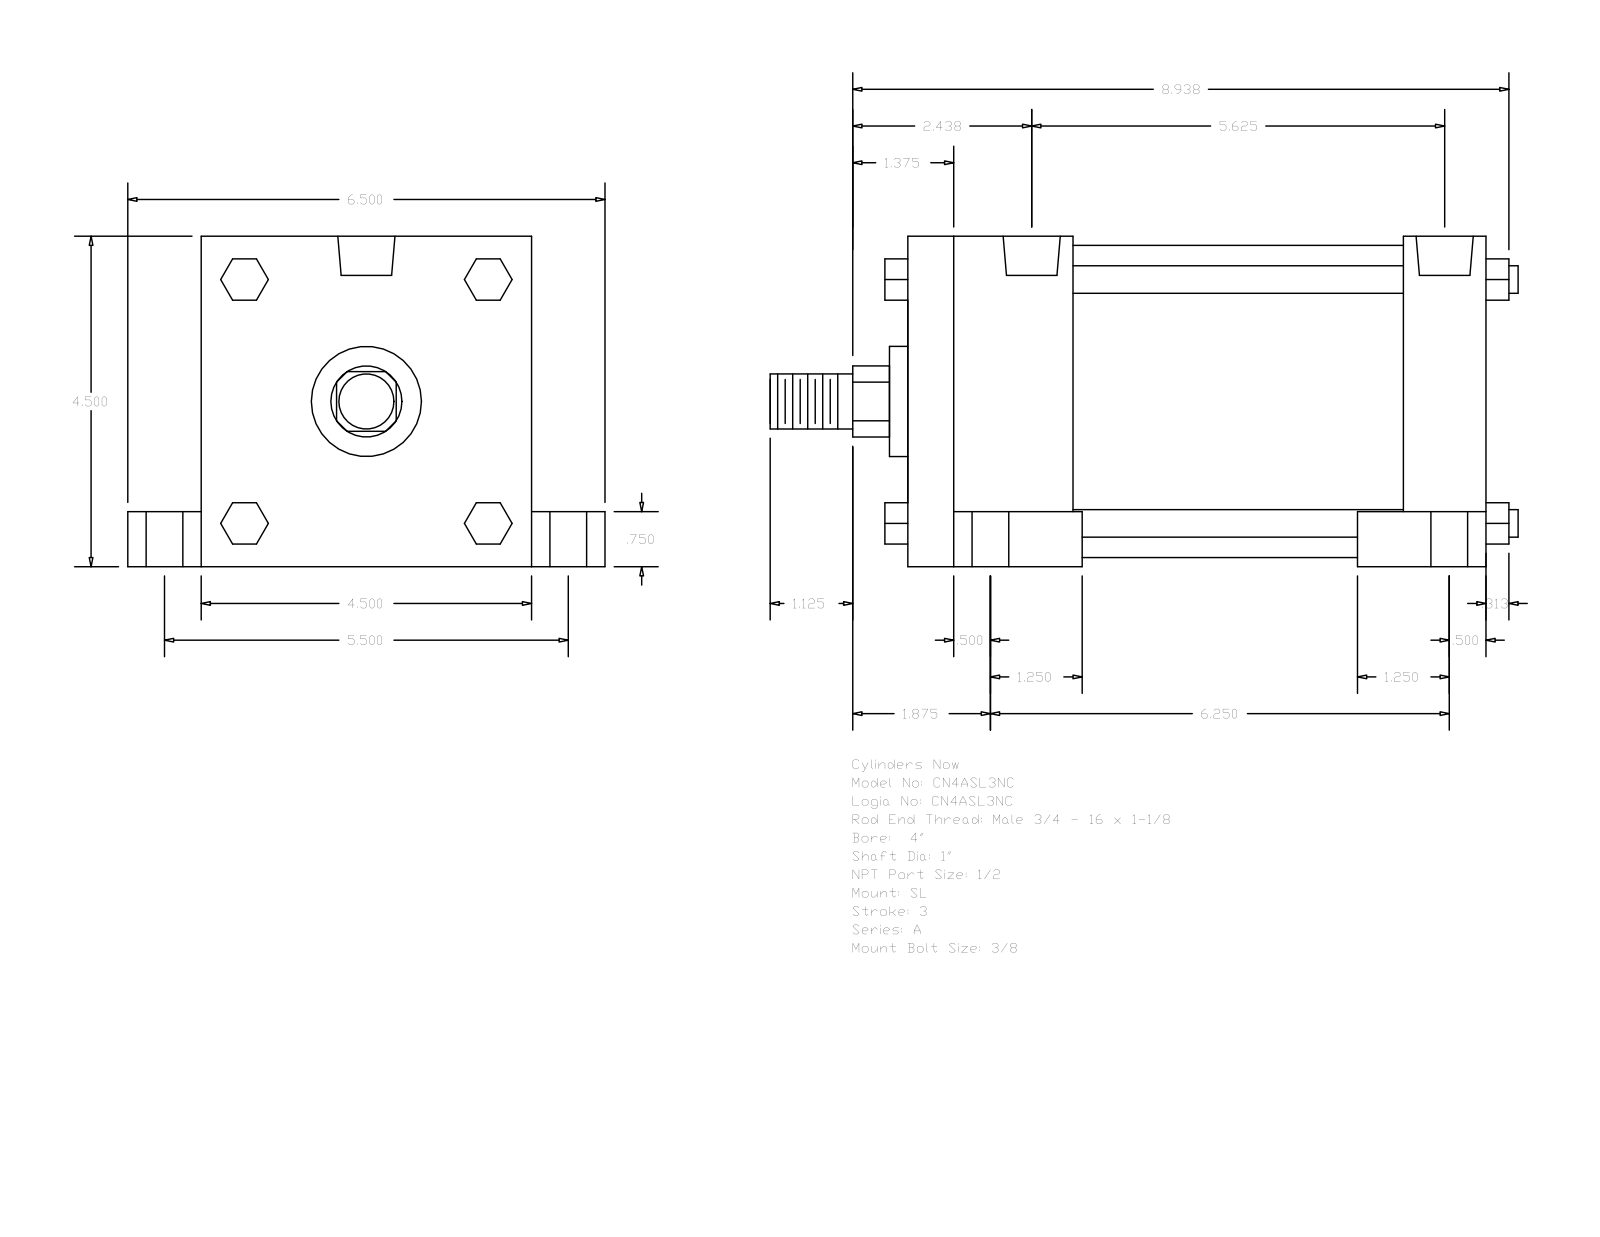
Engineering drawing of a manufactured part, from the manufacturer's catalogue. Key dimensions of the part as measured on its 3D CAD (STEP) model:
Part name (STEP PRODUCT): A_SL__0400_1
STEP written by: GSSL Pune (CONFIG_CONTROL_DESIGN)
Units: millimetres
Bodies: 0 solids, 150 faces (114 planar, 36 cylindrical, 0 other)
Overall size (bounding box): 258.76 × 165.1 × 114.3
Round holes (diameter × count): ⌀8.73 ×4, ⌀12.7 ×4, ⌀19.05 ×4, ⌀19.77 ×2
Round bosses / shafts (diameter × count): ⌀9.53 ×4, ⌀107.95 ×1, ⌀38.1 ×1, ⌀25.4 ×1, ⌀19.05 ×1
Partial cylindrical surfaces — rounded edges, fillets, slot ends (radius × count): R12.29 ×1
Main face-to-face distances: 114.3, 200.02, 139.7, 28.57, 57.15, 142.87, 171.45, 19.05, 25.4, 95.25
Hole centre spacings: 139.7, 3.18, 69.87, 70.01, 71.3, 72, 136.52, 157.61
